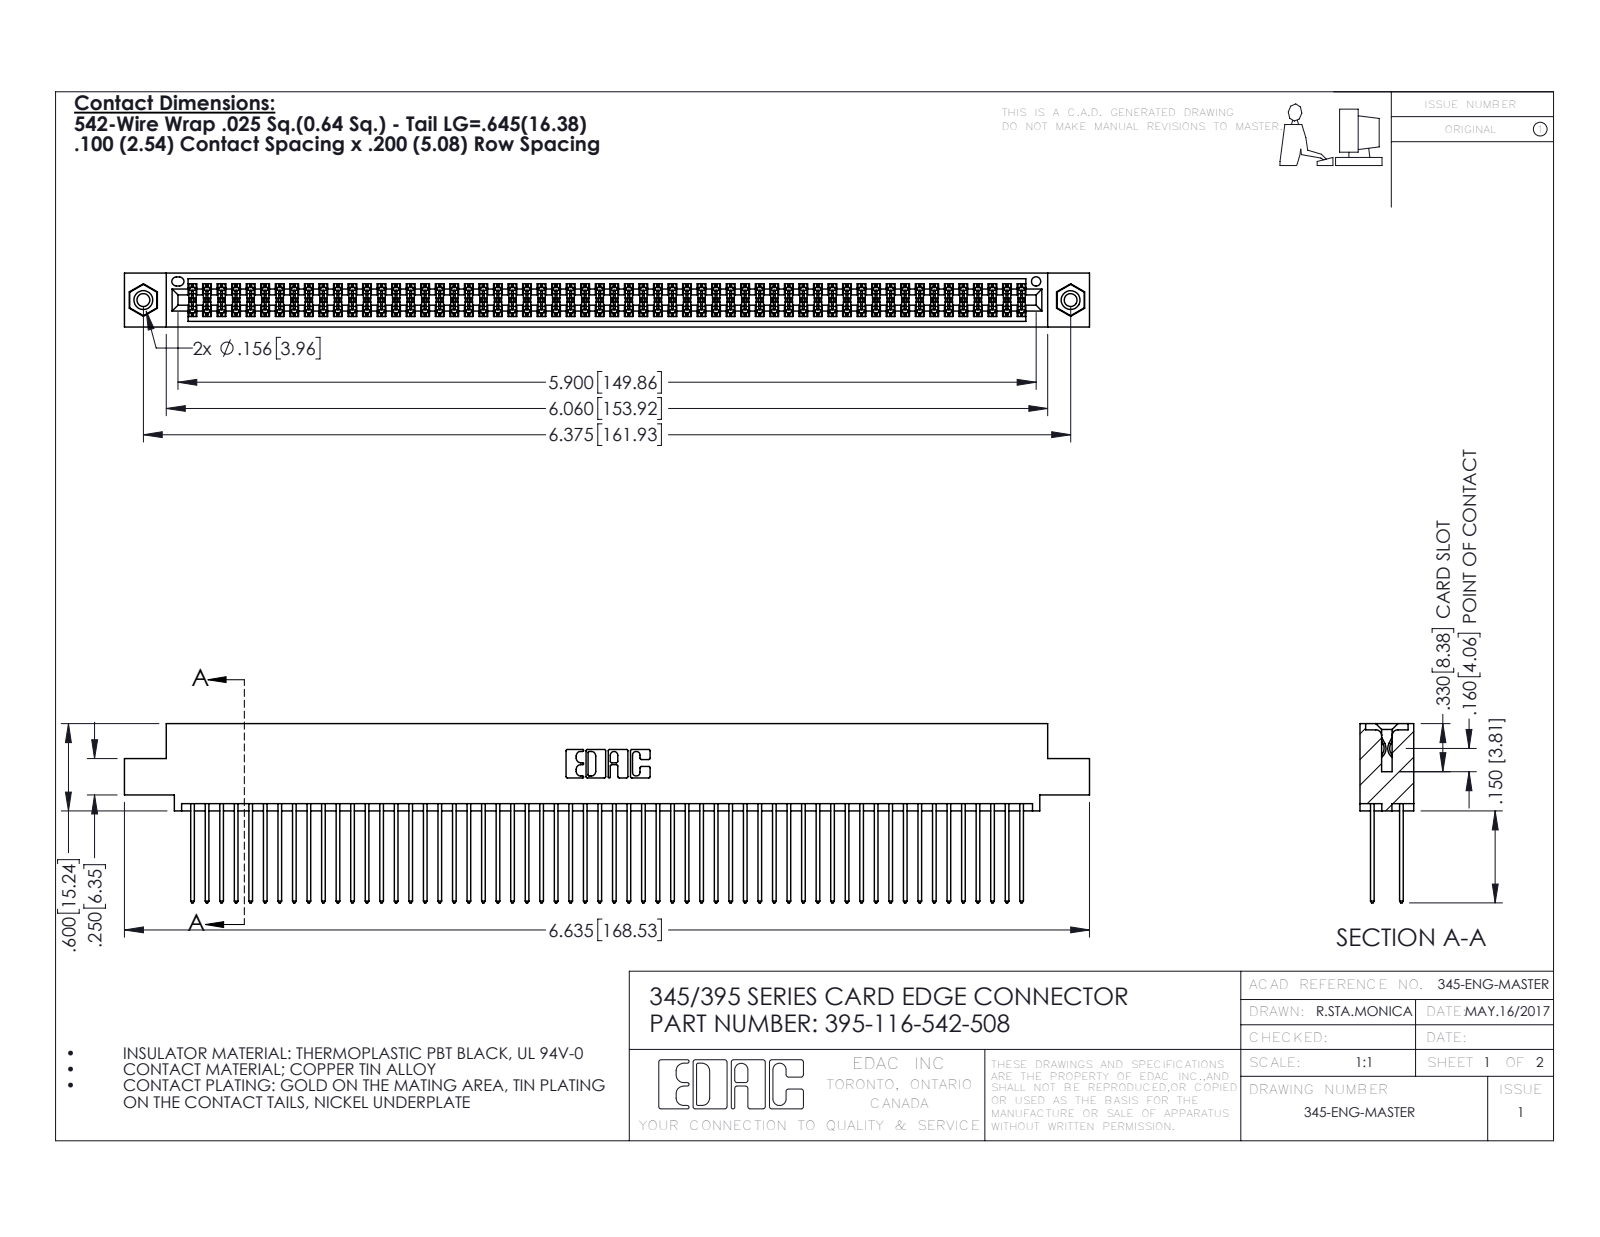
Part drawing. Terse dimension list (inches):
name: 345-250-001_345-250-003-102; 345 Part_0.110 Offset - 0.156 Dia-TI; 345-292-001_345-293-142; 395-116-542-508
written by: SolidWorks 2016 (CONFIG_CONTROL_DESIGN)
unit: in
bodies: 119 solids, 5990 faces (3944 planar, 2030 cylindrical, 16 other)
size: 6.635 × 1.232 × 0.37
volume: 1.036 in³; area: 43.47 in²
holes: 2× ⌀0.089, 2× ⌀0.125, 2× ⌀0.156, 1× ⌀0.064
bosses: 2× ⌀0.155
rounds: 174× R0.006, 116× R0.01, 22× R0.01, 6× R0.007, 6× R0.031, 3× R0.026, 2× R0.014, 2× R0.019
face distances: 0.072, 0.298, 0.2, 0.098, 0.272, 0.025, 0.225, 0.37, 0.175, 0.149
hole spacings: 0.27, 6.139, 6.375
